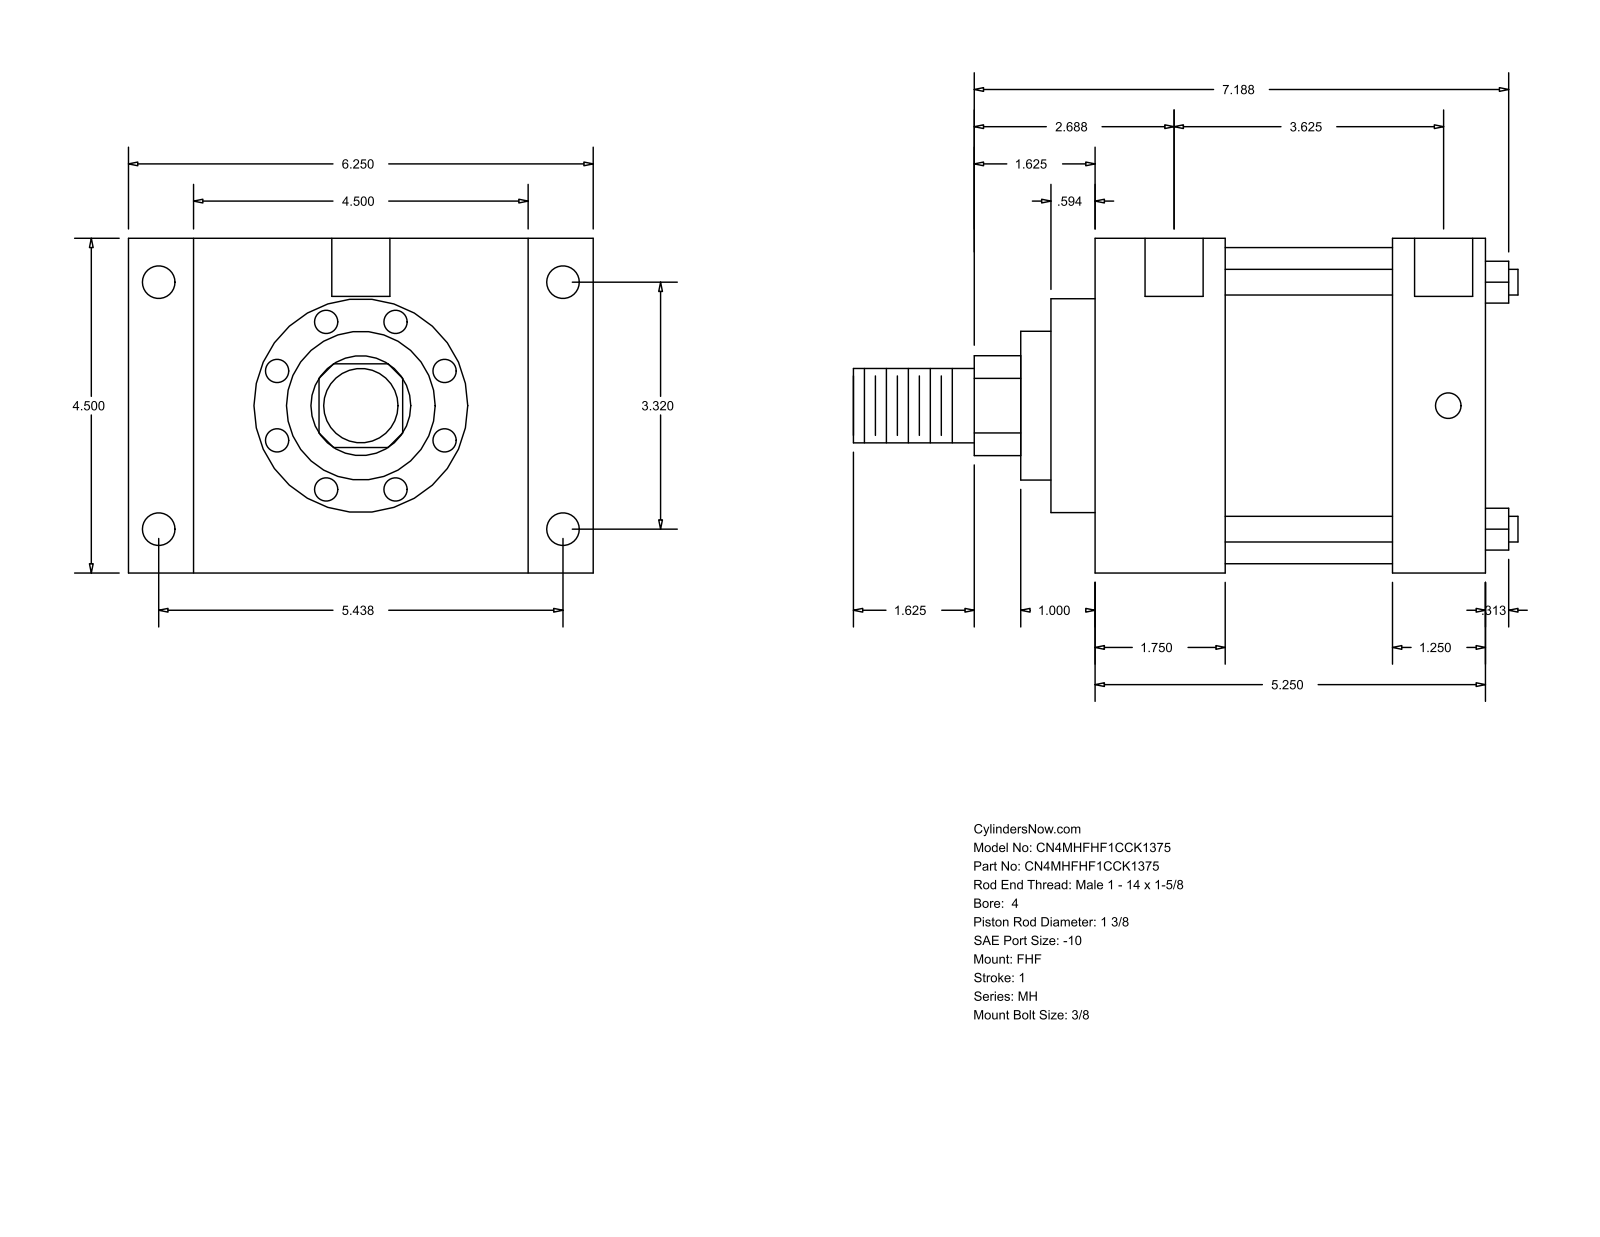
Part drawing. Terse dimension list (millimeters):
name: MH_FHF__0400_1.375
written by: GSSL Pune (CONFIG_CONTROL_DESIGN)
unit: mm
bodies: 0 solids, 90 faces (61 planar, 29 cylindrical, 0 other)
size: 227.01 × 158.75 × 114.3
holes: 4× ⌀8.73, 4× ⌀11.13, 2× ⌀19.84
bosses: 4× ⌀8.76, 1× ⌀107.95, 1× ⌀73.03, 1× ⌀50.8, 1× ⌀34.92, 1× ⌀25.4
rounds: 1× R17.06
face distances: 114.3, 133.35, 44.45, 88.9, 22.23, 136.53, 158.76, 101.61, 57.16, 31.74
hole spacings: 1.59, 84.32, 93.67, 95.26, 138.12, 161.82, 92.08
